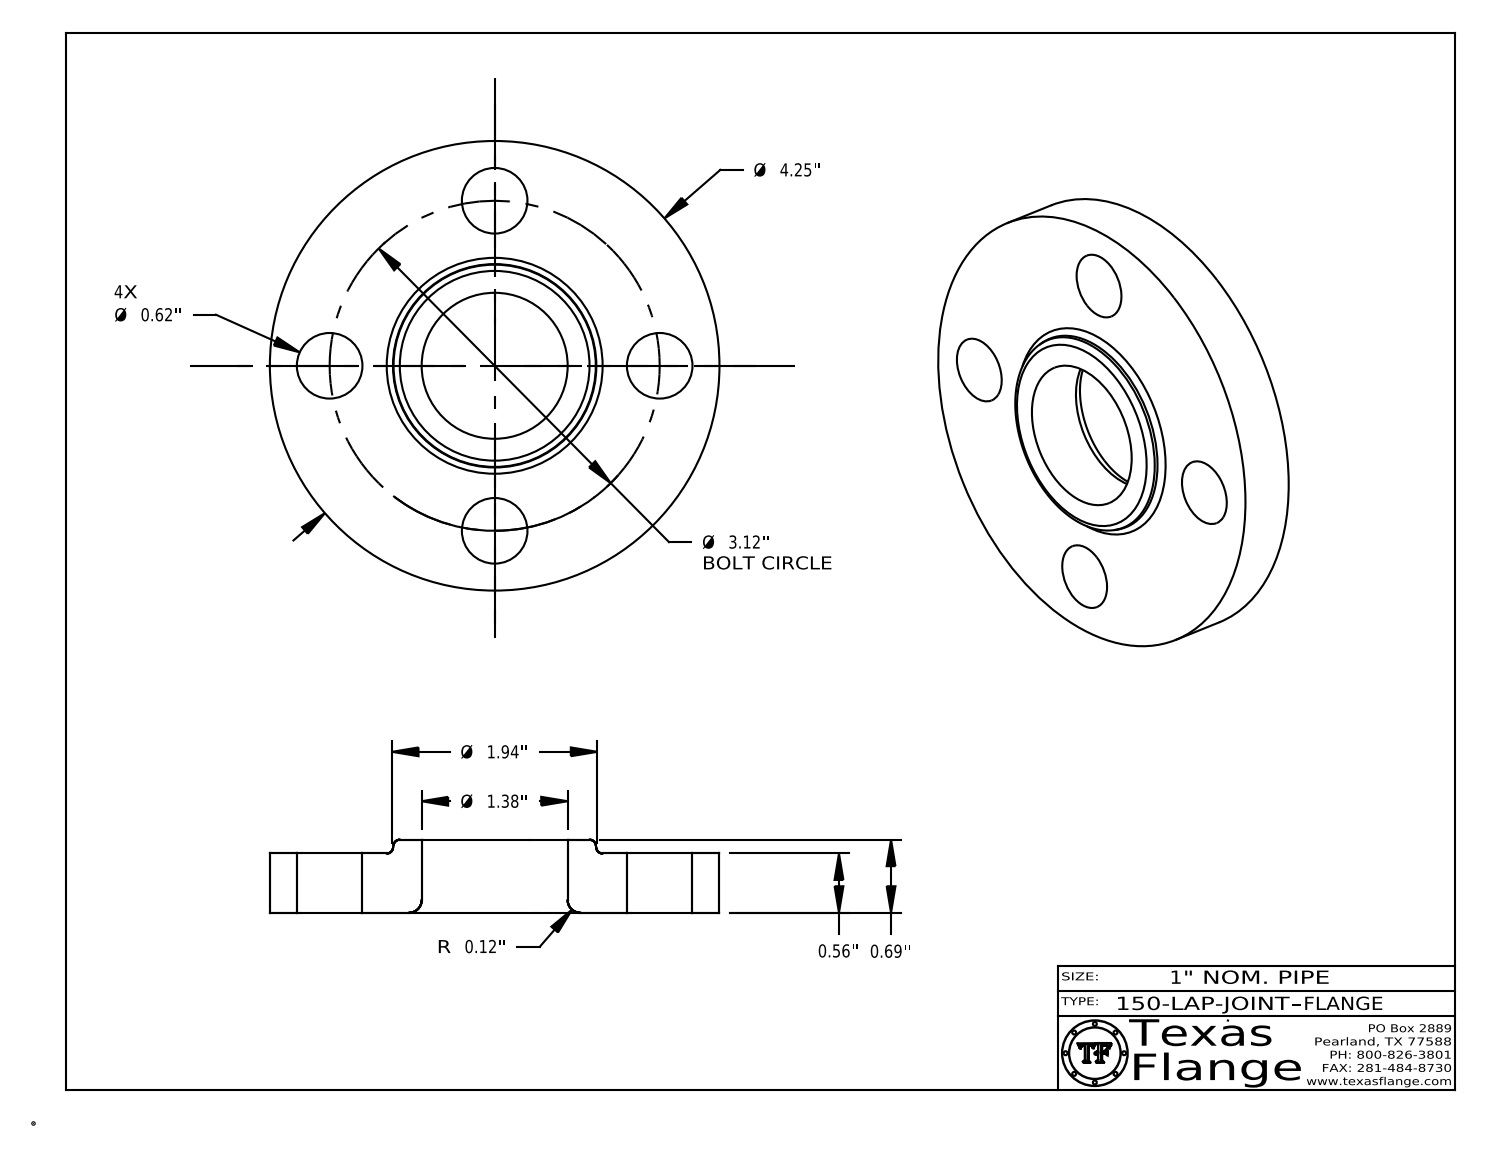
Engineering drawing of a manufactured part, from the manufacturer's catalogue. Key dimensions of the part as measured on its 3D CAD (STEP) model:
Part name (STEP PRODUCT): 150-LAP-JOINT FLANGE
STEP written by: CATIA V5 STEP AP214 (AUTOMOTIVE_DESIGN)
Units: inches
Bodies: 1 solid, 408 faces (368 planar, 32 cylindrical, 8 other)
Overall size (bounding box): 4.25 × 4.25 × 0.69
Volume: 6.596 in³ · Surface area: 38.13 in²
Round holes (diameter × count): ⌀0.62 ×4, ⌀0.495 ×1, ⌀1.38 ×1
Round bosses / shafts (diameter × count): ⌀0.03 ×8, ⌀4.25 ×1, ⌀0.39 ×1
Main face-to-face distances: 0.56, 0.69, 0.13, 0.545, 0.015, 0.145, 0.148, 0.144, 0.027, 0.122
Hole centre spacings: 1.56, 2.206, 1.194, 2.882, 3.12, 1.56
